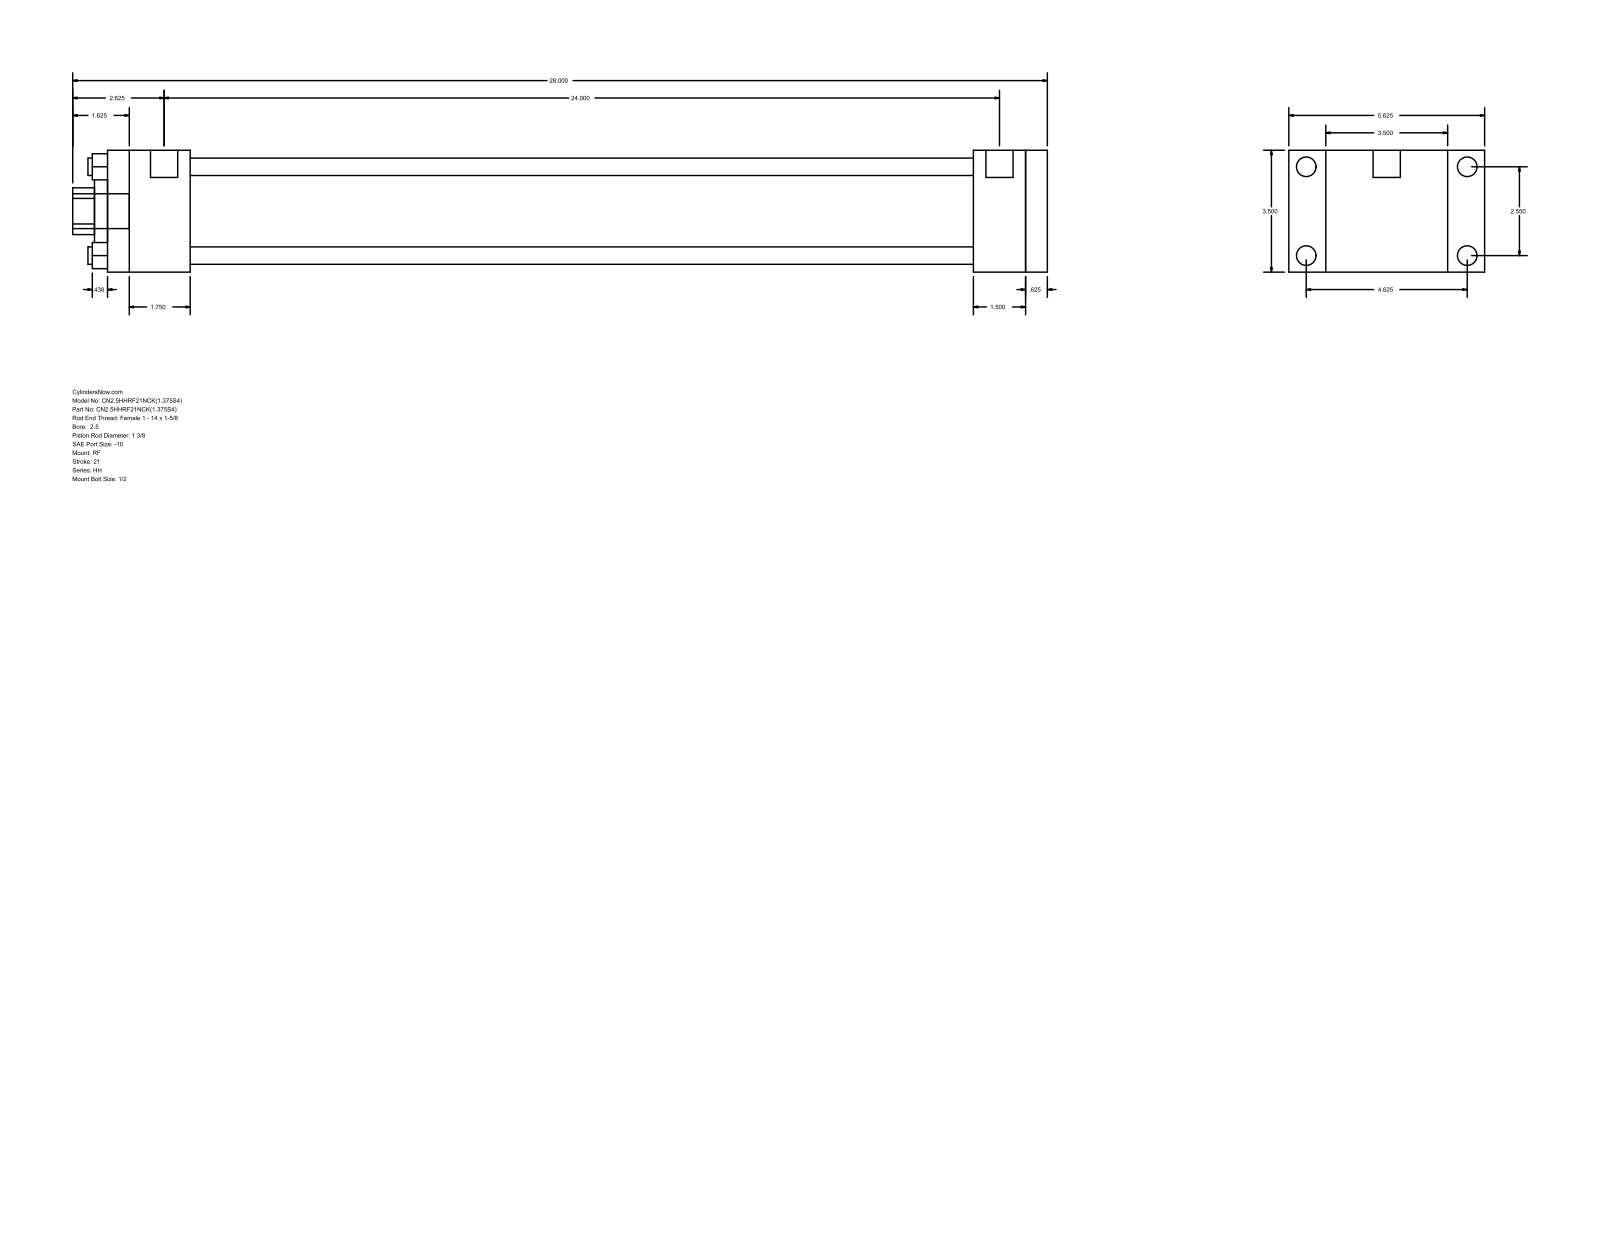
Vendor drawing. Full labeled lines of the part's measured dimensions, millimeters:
Part name (STEP PRODUCT): HH_RF__0250_1.375
STEP written by: GSSL Pune (CONFIG_CONTROL_DESIGN)
Units: millimetres
Bodies: 0 solids, 92 faces (64 planar, 28 cylindrical, 0 other)
Overall size (bounding box): 711.2 × 142.88 × 88.9
Round holes (diameter × count): ⌀12.7 ×4, ⌀34.92 ×1, ⌀50.8 ×1, ⌀73.03 ×1
Round bosses / shafts (diameter × count): ⌀14.3 ×4, ⌀5.56 ×4, ⌀19.84 ×2, ⌀25.4 ×1
Partial cylindrical surfaces — rounded edges, fillets, slot ends (radius × count): R17.06 ×1
Main face-to-face distances: 88.9, 15.87, 669.93, 685.8, 60.32, 609.61, 625.48, 631.83, 571.51, 38.1
Hole centre spacings: 45.79, 64.76, 91.58
